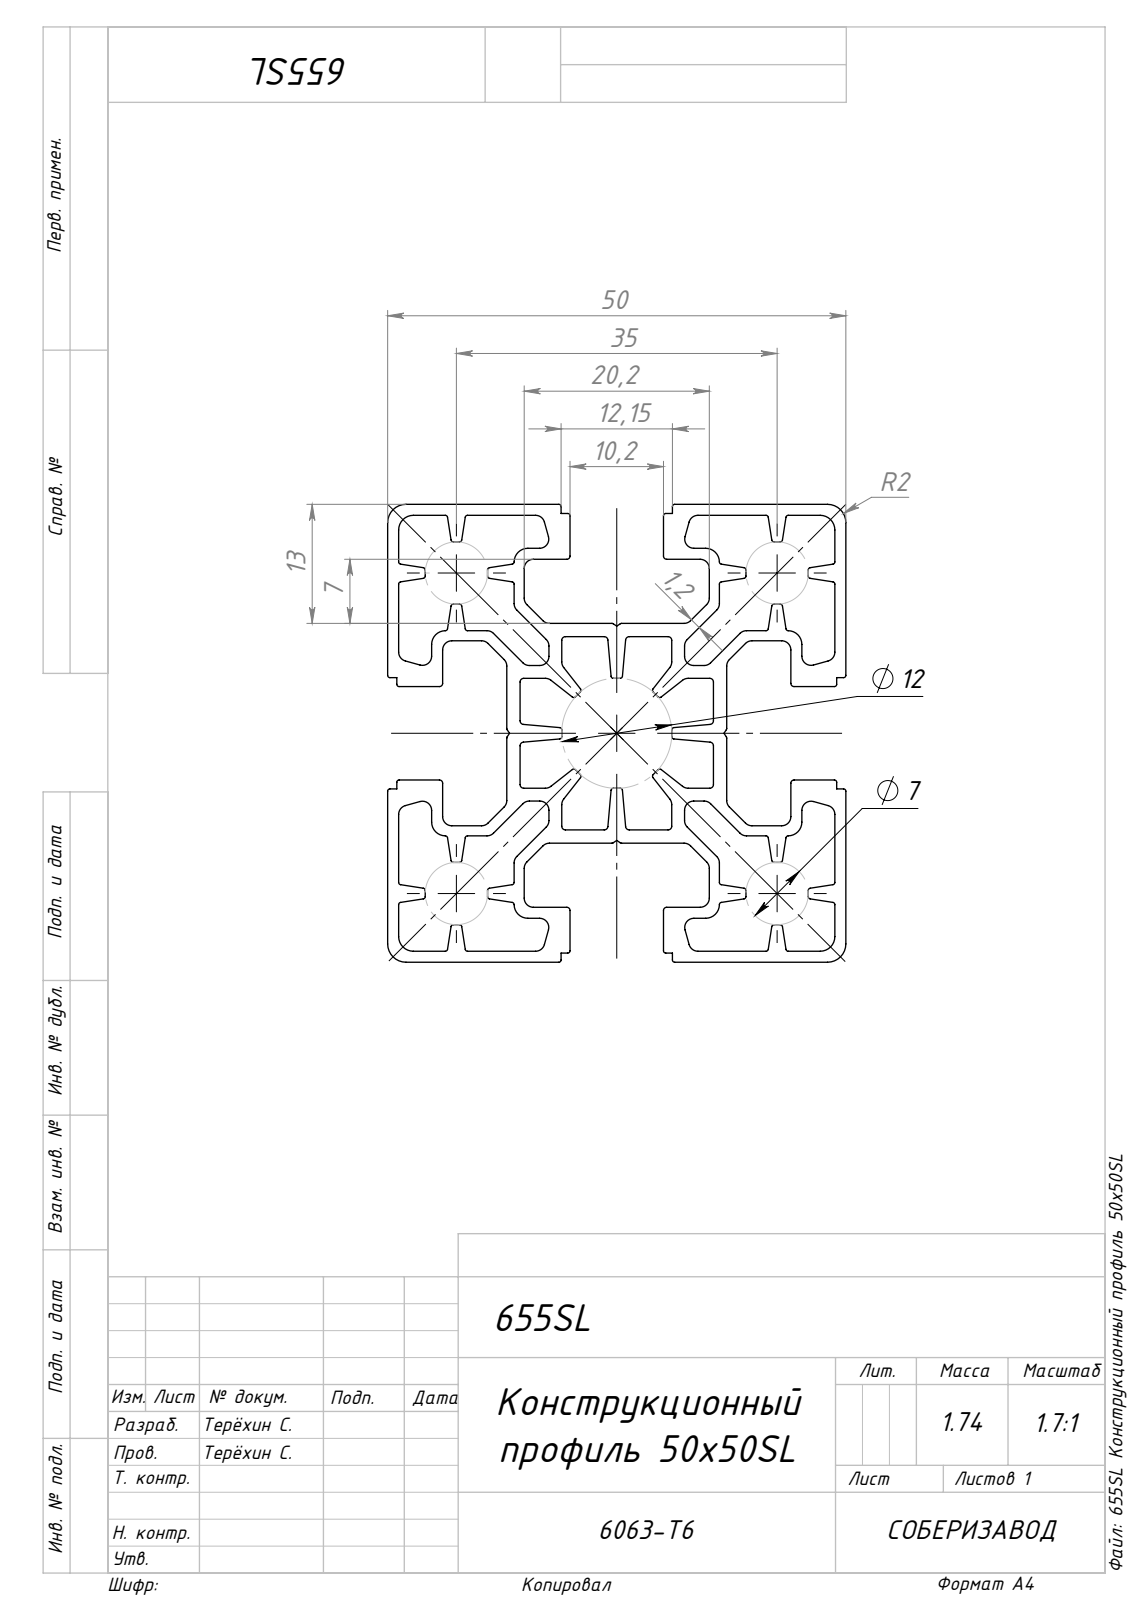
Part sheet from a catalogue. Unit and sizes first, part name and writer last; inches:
Units: inches
Overall size (bounding box): 39.37 × 1.969 × 1.969
Partial cylindrical surfaces — rounded edges, fillets, slot ends (radius × count): R0.01 ×104, R0.039 ×68, R0.016 ×16, R0.014 ×8, R0.059 ×8, R0.063 ×4, R0.079 ×4
Main face-to-face distances: 0.047, 1.921, 0.512, 1.969, 0.236, 0.189, 1.457, 0.465, 1.409, 1.22
Volume: 39.44 in³ · Surface area: 1 332 in²
Bodies: 1 solid, 438 faces (218 planar, 220 cylindrical, 0 other)
STEP written by: SolidWorks 2019 (AUTOMOTIVE_DESIGN)
